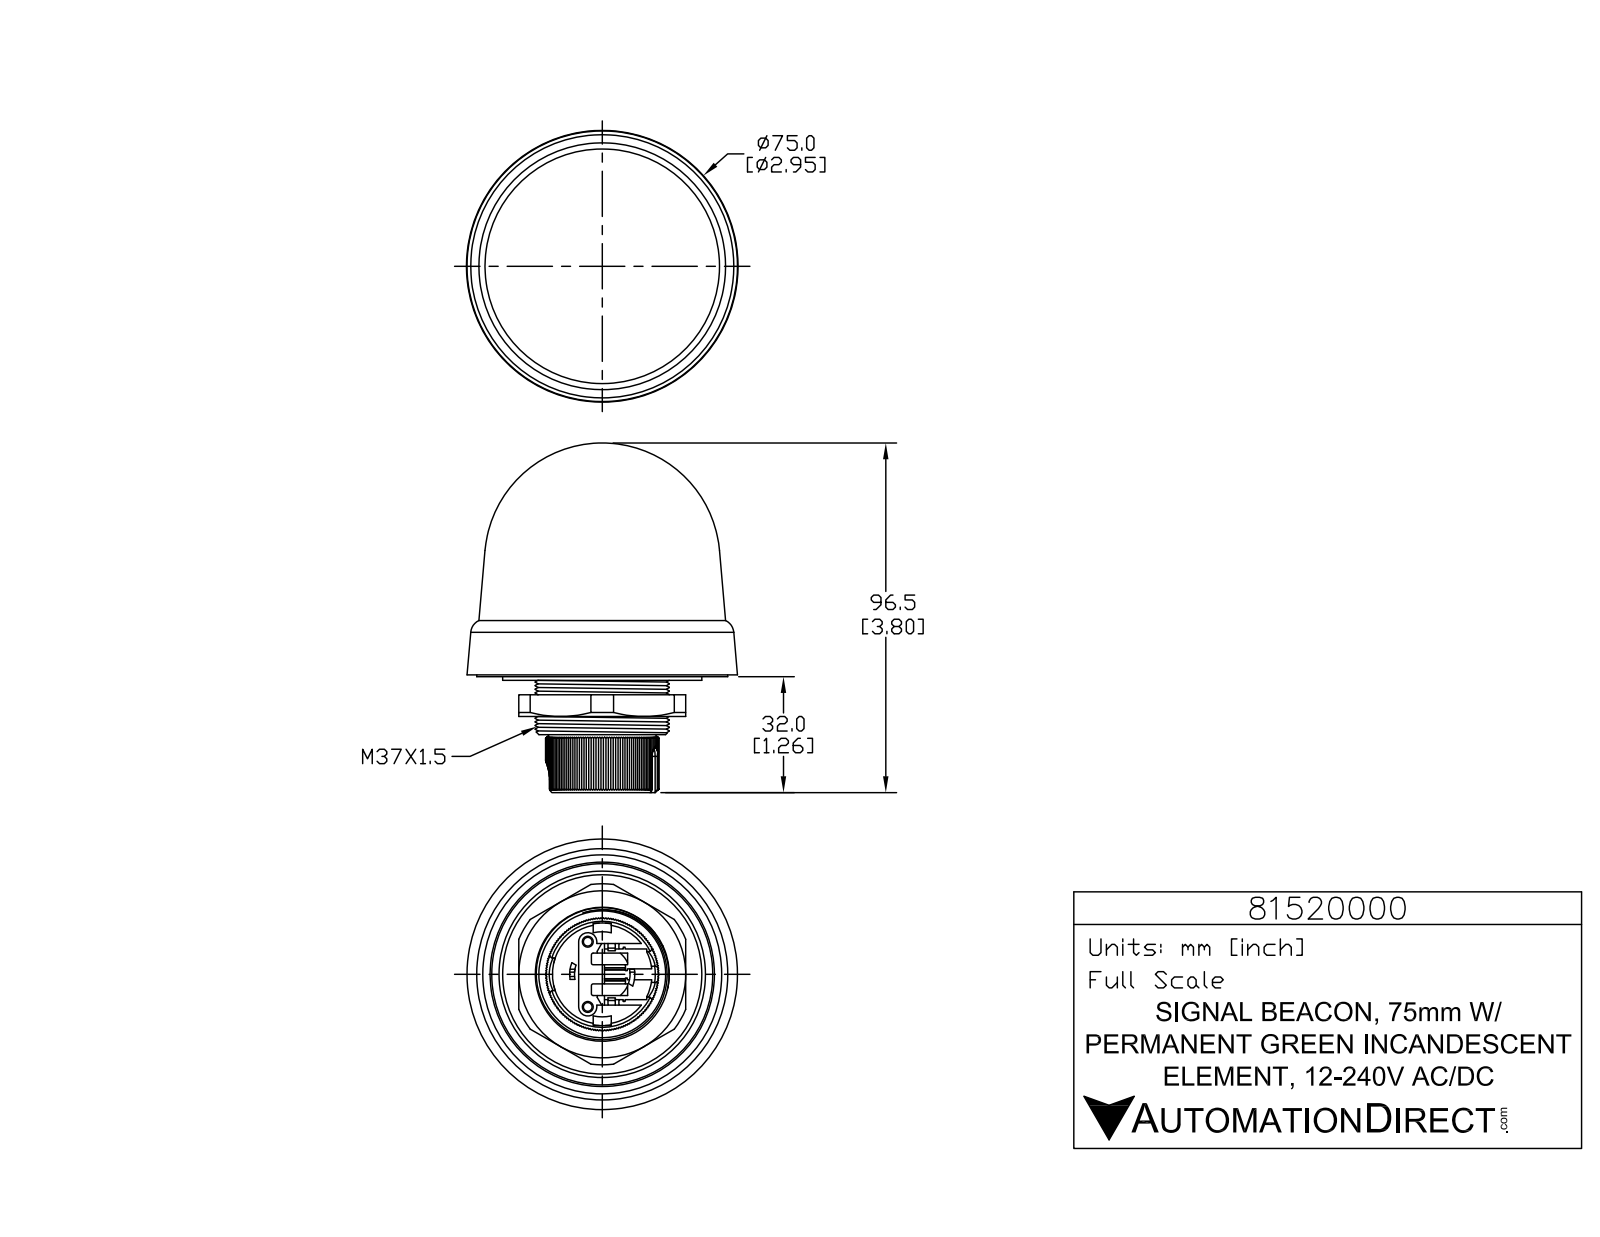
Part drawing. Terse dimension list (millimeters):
name: 81520000
written by: SolidWorks 2019 (CONFIG_CONTROL_DESIGN)
unit: mm
bodies: 3 solids, 560 faces (432 planar, 80 cylindrical, 48 other)
size: 96.5 × 74.7 × 74.7
volume: 202 500 mm³; area: 37 860 mm²
holes: 2× ⌀2.4, 2× ⌀3, 1× ⌀15.3, 1× ⌀29
bosses: 2× ⌀5.5, 2× ⌀1.7, 1× ⌀55, 1× ⌀37, 1× ⌀23.5
rounds: 6× R0.2, 6× R1, 4× R0.5, 2× R0.8, 2× R2, 2× R2.5, 1× R4.5, 1× R9
face distances: 4.5, 9, 5, 11, 13, 8.5, 1.5, 10, 3, 4
hole spacings: 9.9, 18
